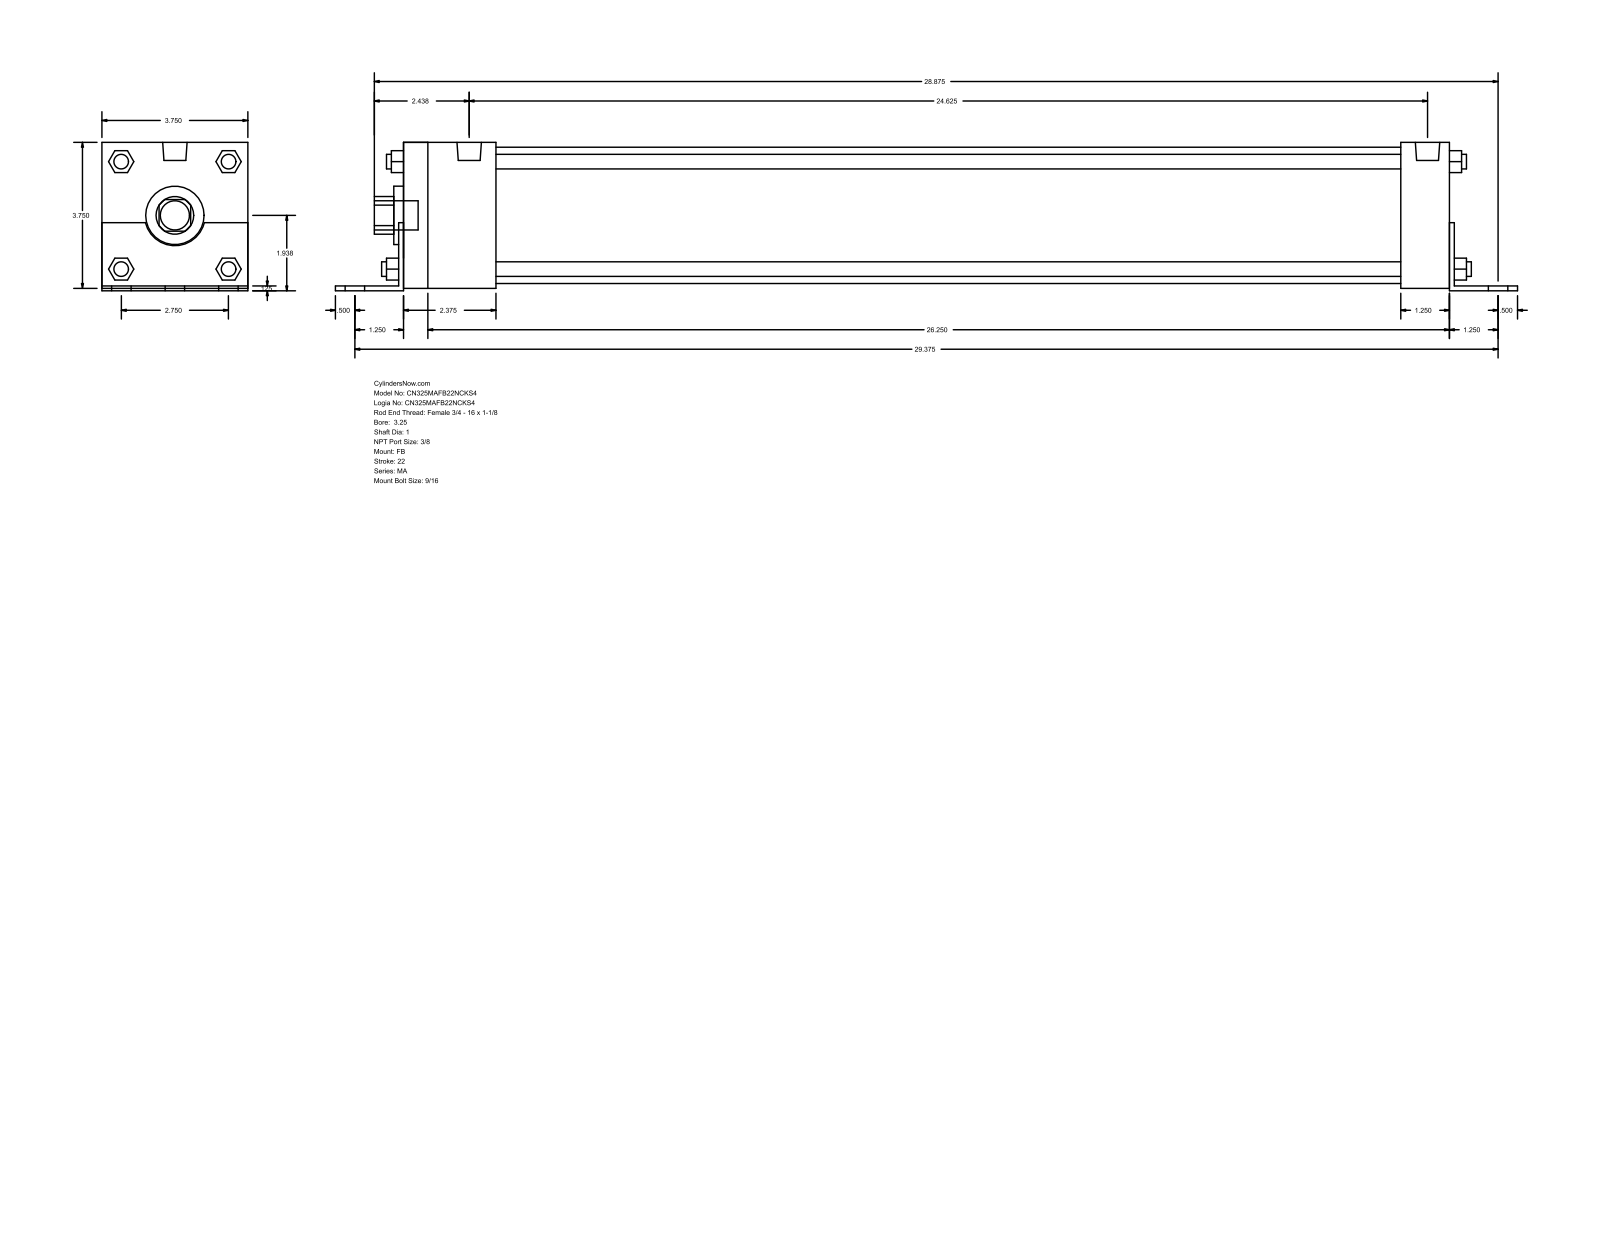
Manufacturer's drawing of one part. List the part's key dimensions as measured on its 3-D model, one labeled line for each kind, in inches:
Part name (STEP PRODUCT): MA_FB__0325_1
STEP written by: GSSL Pune (CONFIG_CONTROL_DESIGN)
Units: inches
Bodies: 0 solids, 140 faces (105 planar, 35 cylindrical, 0 other)
Overall size (bounding box): 30.375 × 3.813 × 3.75
Round holes (diameter × count): ⌀1 ×1, ⌀1.5 ×1, ⌀3.5 ×1
Round bosses / shafts (diameter × count): ⌀0.563 ×6, ⌀0.437 ×4, ⌀0.375 ×4, ⌀0.627 ×2, ⌀0.75 ×1
Partial cylindrical surfaces — rounded edges, fillets, slot ends (radius × count): R0.484 ×1, R0.78 ×1
Main face-to-face distances: 3.75, 0.125, 0.063, 3.812, 0.062, 3.687, 0.125, 26.875, 27.125, 27
